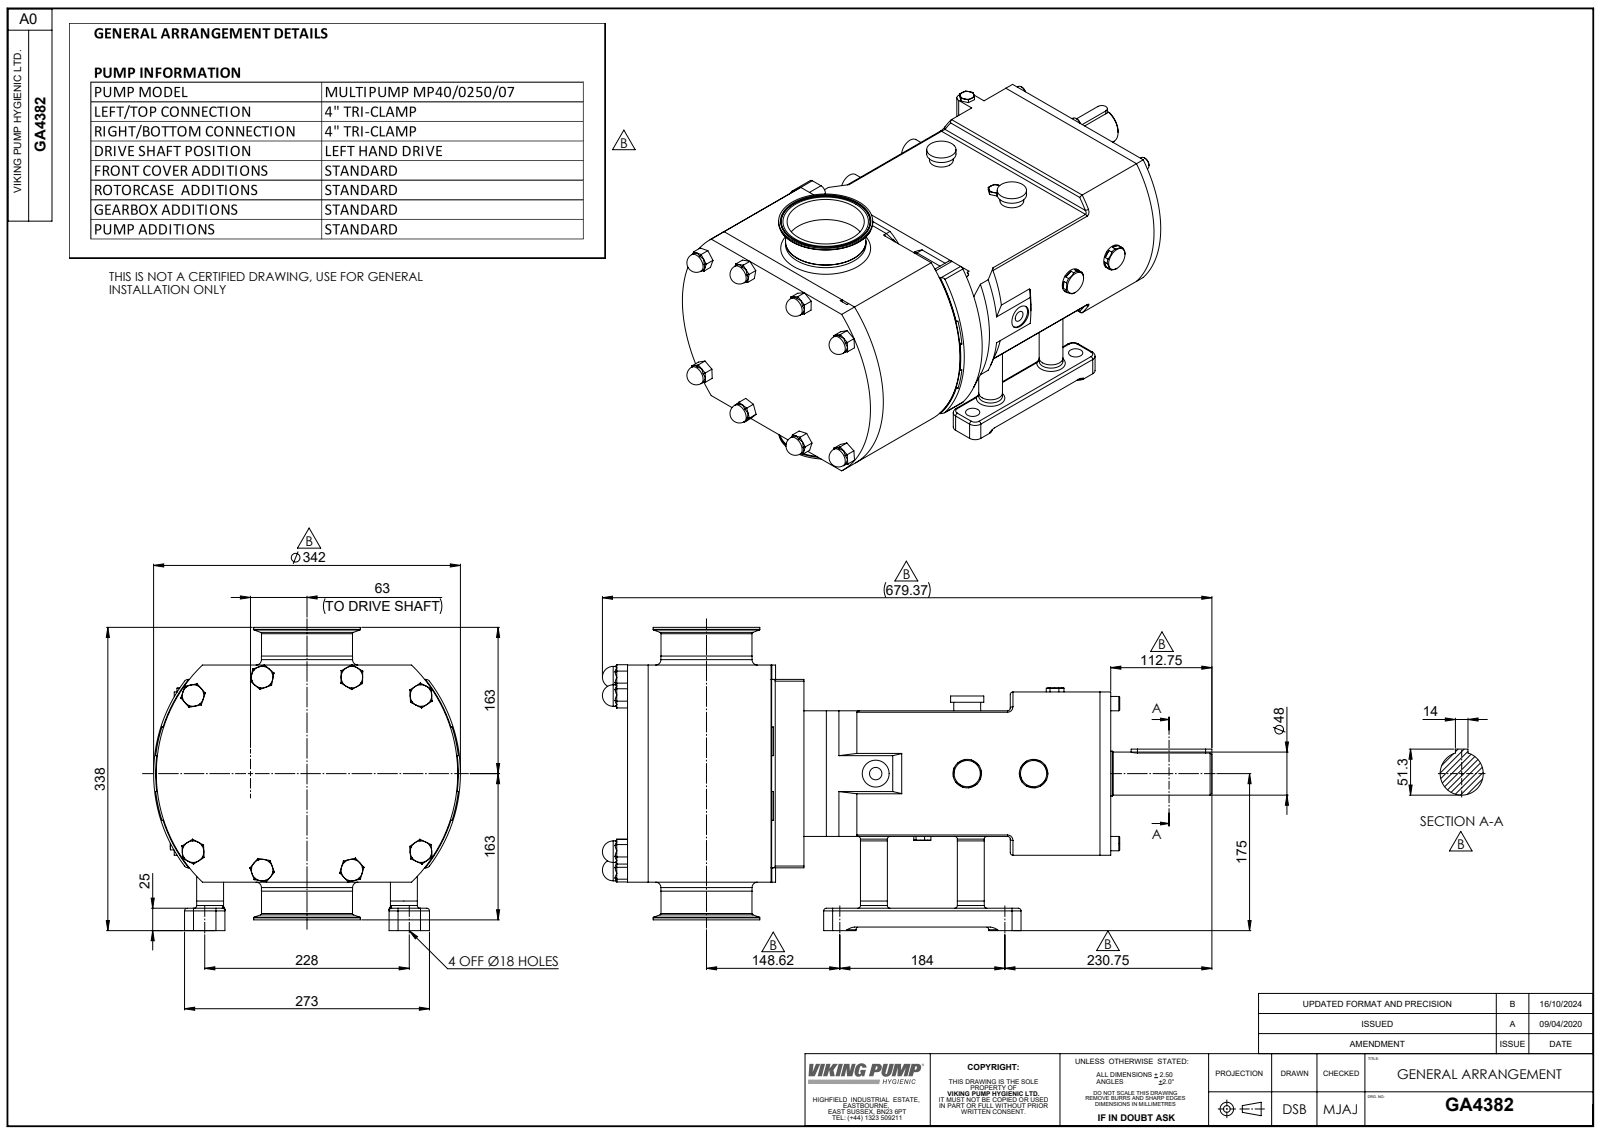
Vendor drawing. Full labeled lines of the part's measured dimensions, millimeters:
Part name (STEP PRODUCT): Copy of Z94-5121-66 - 4 INCH^GA4382; GA4382; Copy of CP40L-0250 V LHD^GA4382
STEP written by: SolidWorks 2023 (AUTOMOTIVE_DESIGN)
Units: millimetres
Bodies: 3 solids, 965 faces (365 planar, 279 cylindrical, 321 other)
Overall size (bounding box): 679.37 × 342 × 338
Volume: 28 910 000 mm³ · Surface area: 979 040 mm²
Round holes (diameter × count): ⌀10.2 ×4, ⌀18 ×4, ⌀11.89 ×2, ⌀35 ×2, ⌀13.83 ×1, ⌀30 ×1, ⌀97.5 ×1
Round bosses / shafts (diameter × count): ⌀30 ×10, ⌀24 ×8, ⌀16 ×6, ⌀110 ×2, ⌀70 ×2, ⌀37 ×2, ⌀31.75 ×2, ⌀250 ×1
Partial cylindrical surfaces — rounded edges, fillets, slot ends (radius × count): R10 ×24, R3 ×22, R8 ×20, R6 ×10, R5 ×4, R11 ×4, R7 ×2, R15.24 ×2
Main face-to-face distances: 21, 51, 191, 30, 212, 161, 140, 538.62, 242, 182
Hole centre spacings: 108, 54.04, 78.08, 109.45, 118.96, 126, 152.74, 184
